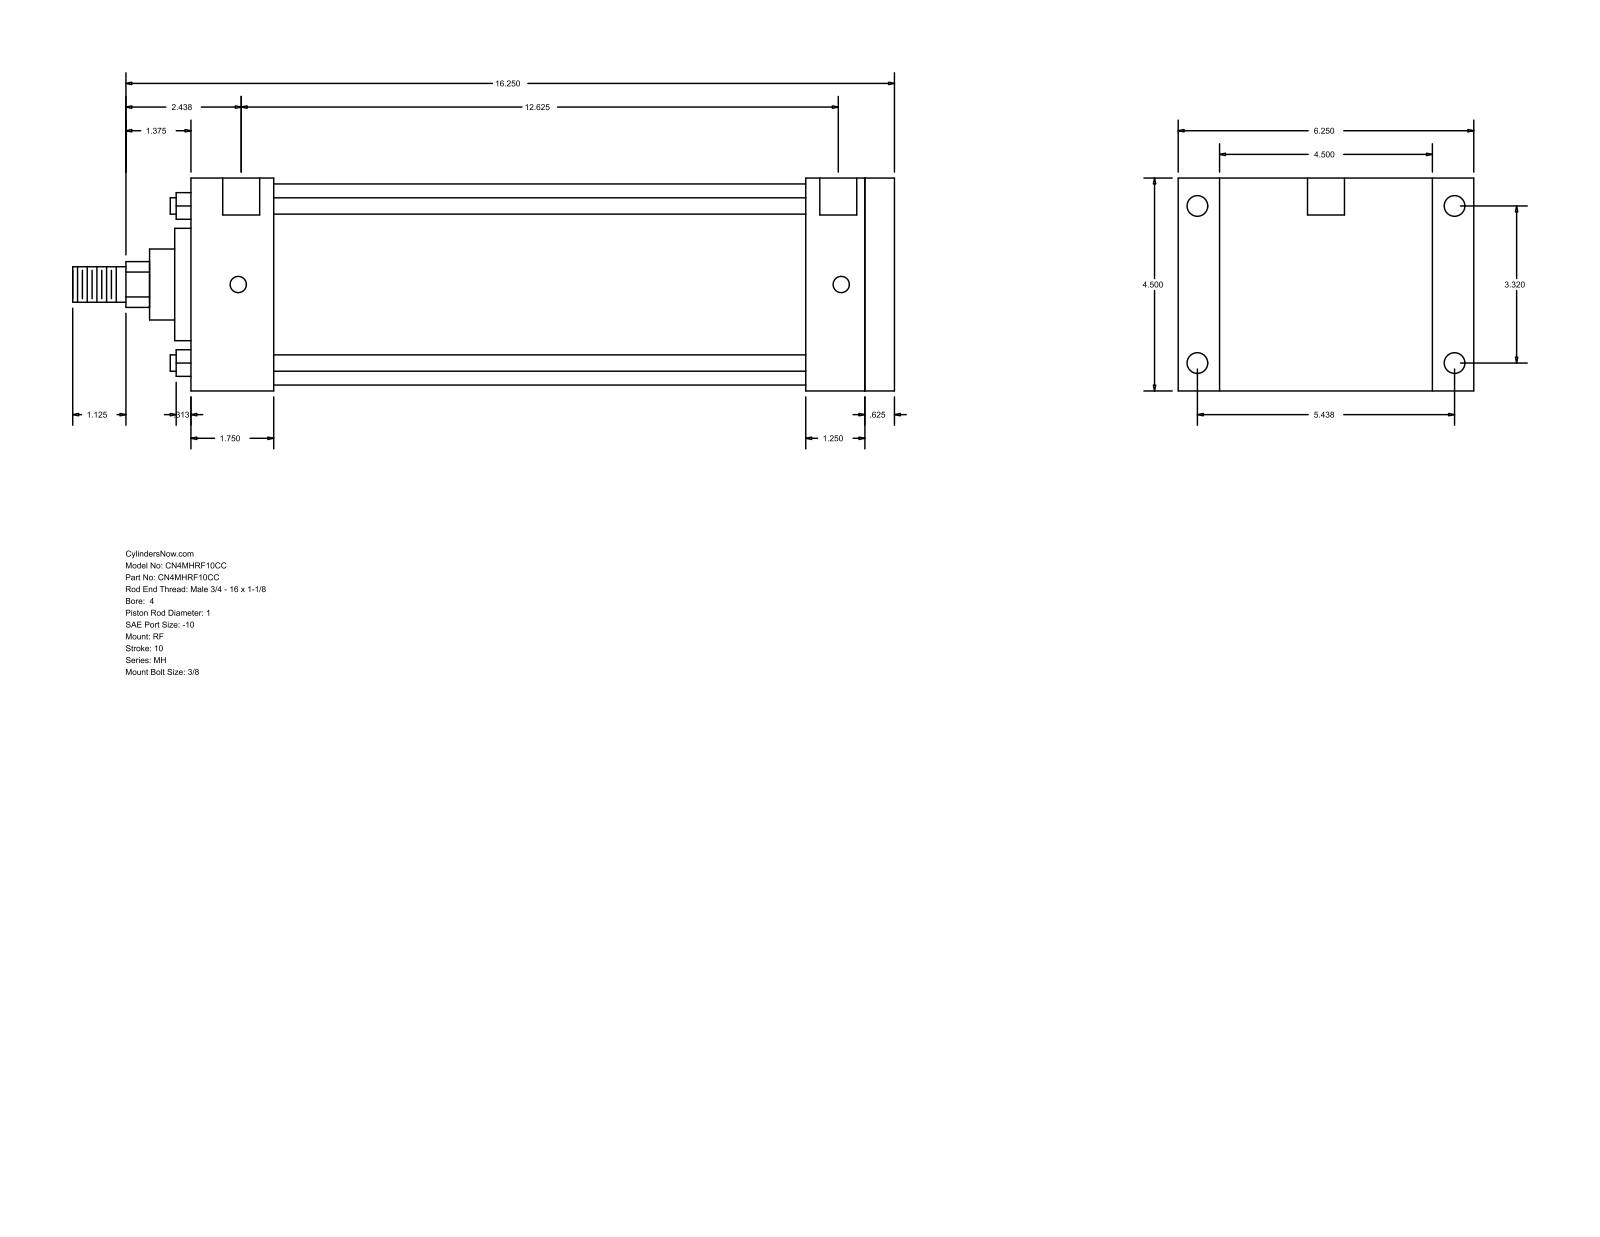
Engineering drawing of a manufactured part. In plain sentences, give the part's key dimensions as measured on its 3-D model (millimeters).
The part is named "MH_RF__0400_1". Its 3-D file was written by "GSSL Pune (CONFIG_CONTROL_DESIGN)". It is 0 solids with 94 faces: 65 planar, 29 cylindrical and 0 other. Overall it measures 441.32 by 158.75 by 114.3 millimeters. Round holes: 4 of diameter 8.73, 4 of diameter 11.13, 2 of diameter 19.84. Round bosses or shafts: 4 of diameter 8.76, 1 of diameter 107.95, 1 of diameter 60.33, 1 of diameter 38.1, 1 of diameter 25.4, 1 of diameter 19.05. Partial cylindrical surfaces (rounded edges, fillets, slot ends): 1 of radius 12.29. The main face-to-face distances are 114.3, 377.83, 361.96, 15.87, 47.63, 44.46, 317.5, 333.37, 330.2, 285.74. The hole center spacings are 84.32, 138.12, 161.82, 323.85, 1.58, 1.59, 320.68, 322.26.
